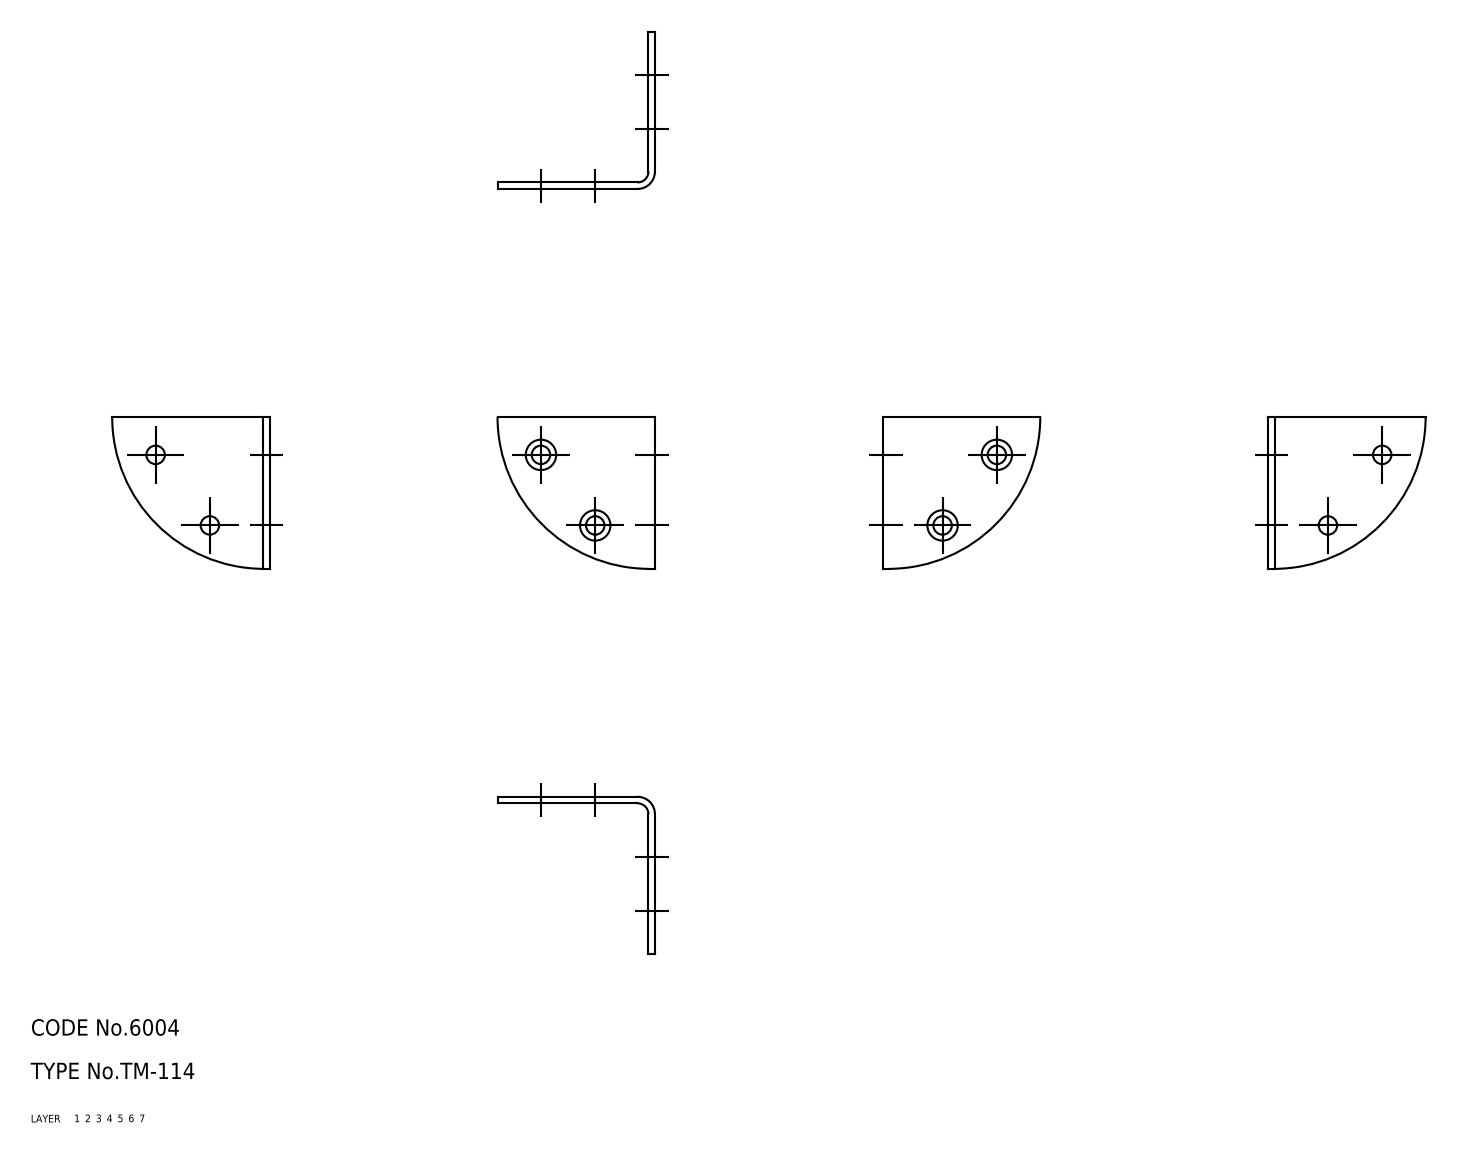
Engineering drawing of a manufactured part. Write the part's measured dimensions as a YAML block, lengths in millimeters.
part_name: "angle"
step_written_by: "CADfix (AUTOMOTIVE_DESIGN)"
units: millimeters
bodies: {solids: 1, faces: 26, planar: 0, cylindrical: 0, other: 26}
overall_size: [29, 29, 28]
volume: 1392
surface_area: 2575
